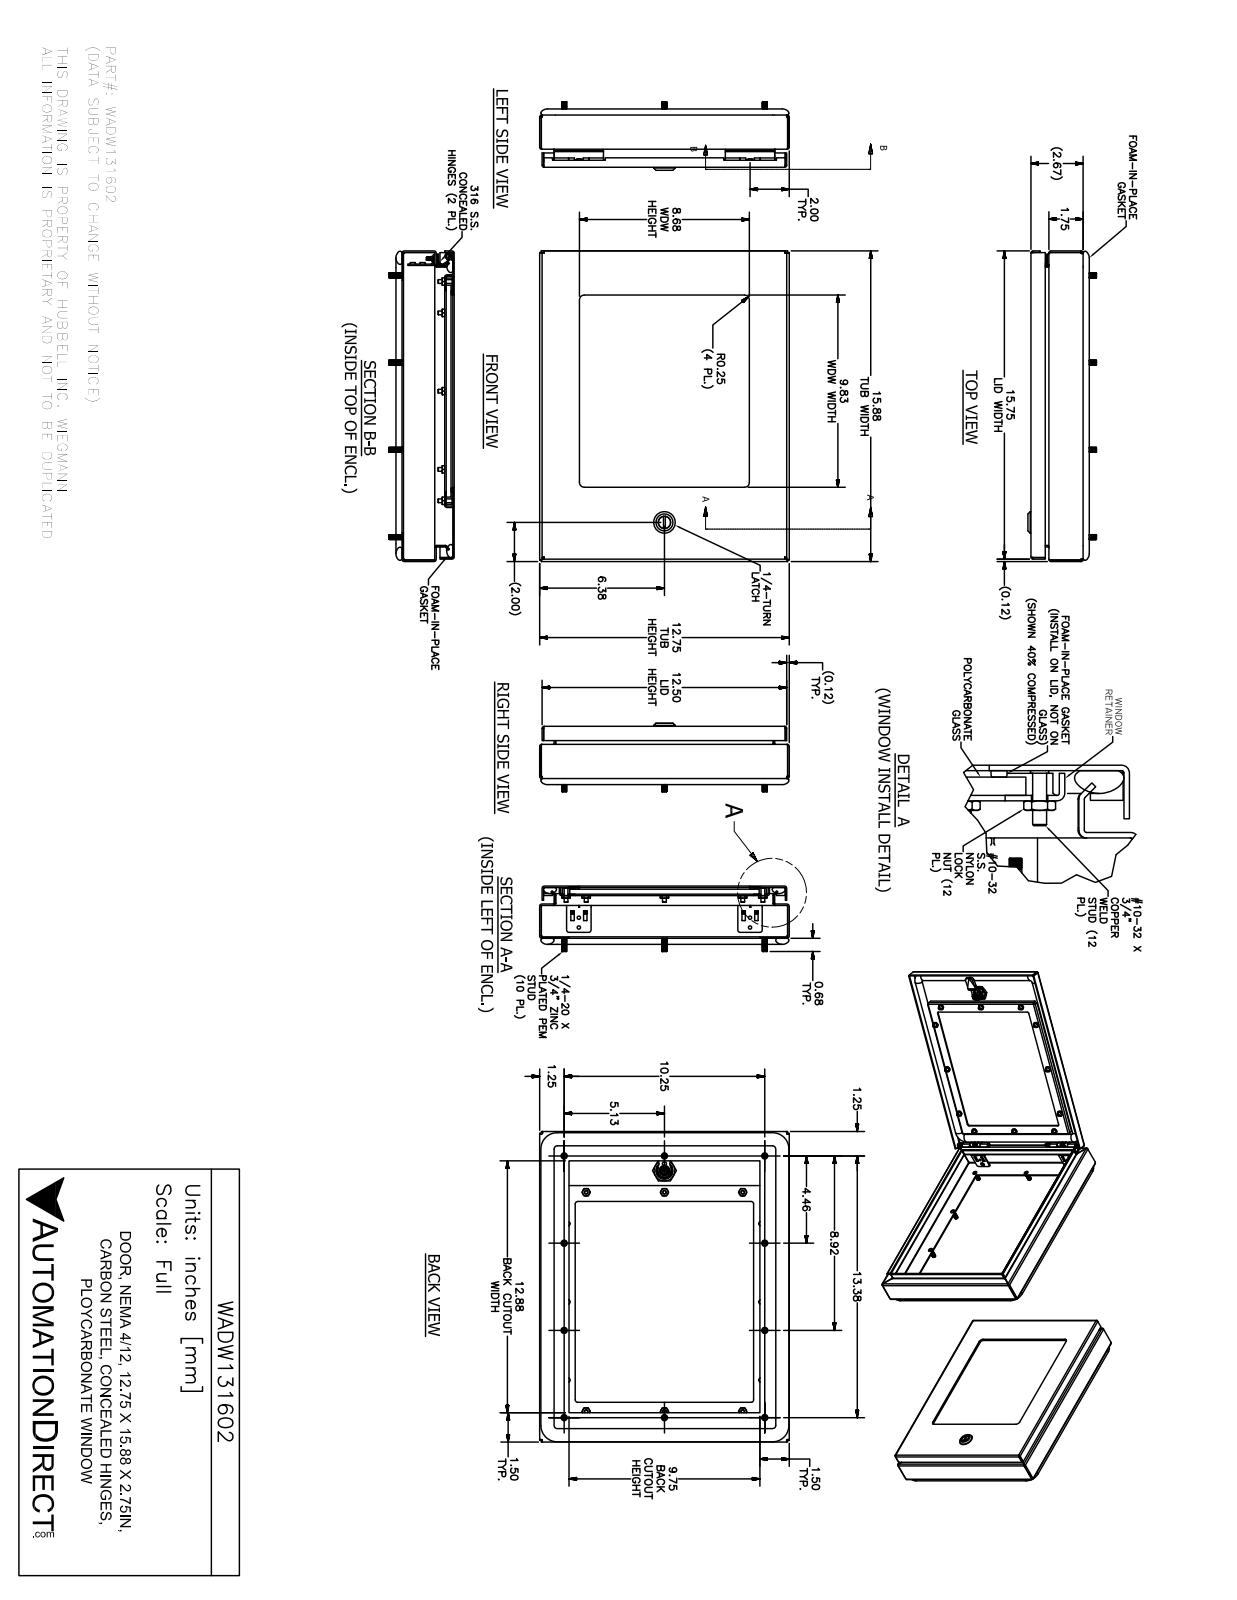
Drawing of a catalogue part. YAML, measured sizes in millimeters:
part_name: "WADW131602"
step_written_by: "SolidWorks 2017 (AUTOMOTIVE_DESIGN)"
units: millimeters
bodies: {solids: 65, faces: 1951, planar: 724, cylindrical: 625, other: 602}
overall_size: [403.2, 323.9, 88.9]
volume: 1305000
surface_area: 857400
round_holes:
  - {diameter: 4, count: 14}
  - {diameter: 7.1, count: 12}
  - {diameter: 6.3, count: 9}
  - {diameter: 2.4, count: 4}
  - {diameter: 3.9, count: 4}
  - {diameter: 4.2, count: 4}
  - {diameter: 4.4, count: 4}
  - {diameter: 4.8, count: 4}
  - {diameter: 4.7, count: 1}
  - {diameter: 5, count: 1}
  - {diameter: 8, count: 1}
  - {diameter: 10, count: 1}
round_bosses_or_shafts:
  - {diameter: 6.4, count: 20}
  - {diameter: 4.8, count: 12}
  - {diameter: 9.1, count: 4}
  - {diameter: 8.1, count: 4}
  - {diameter: 6.5, count: 4}
  - {diameter: 4.2, count: 4}
  - {diameter: 3.3, count: 4}
  - {diameter: 28, count: 1}
partial_cylinders:
  - {radius: 0.8, count: 34}
  - {radius: 0.3, count: 30}
  - {radius: 1.3, count: 26}
  - {radius: 2.7, count: 24}
  - {radius: 3.2, count: 20}
  - {radius: 0.4, count: 18}
  - {radius: 0.5, count: 13}
  - {radius: 0.8, count: 8}
face_to_face_distances: [1.9, 10.4, 8.6, 65.9, 6.4, 2.2, 4.1, 55.4, 42.6, 61.8]
hole_center_spacings: [101.6, 113.2, 283.9, 222.1, 172.1, 203.2, 226.5, 248.3]
